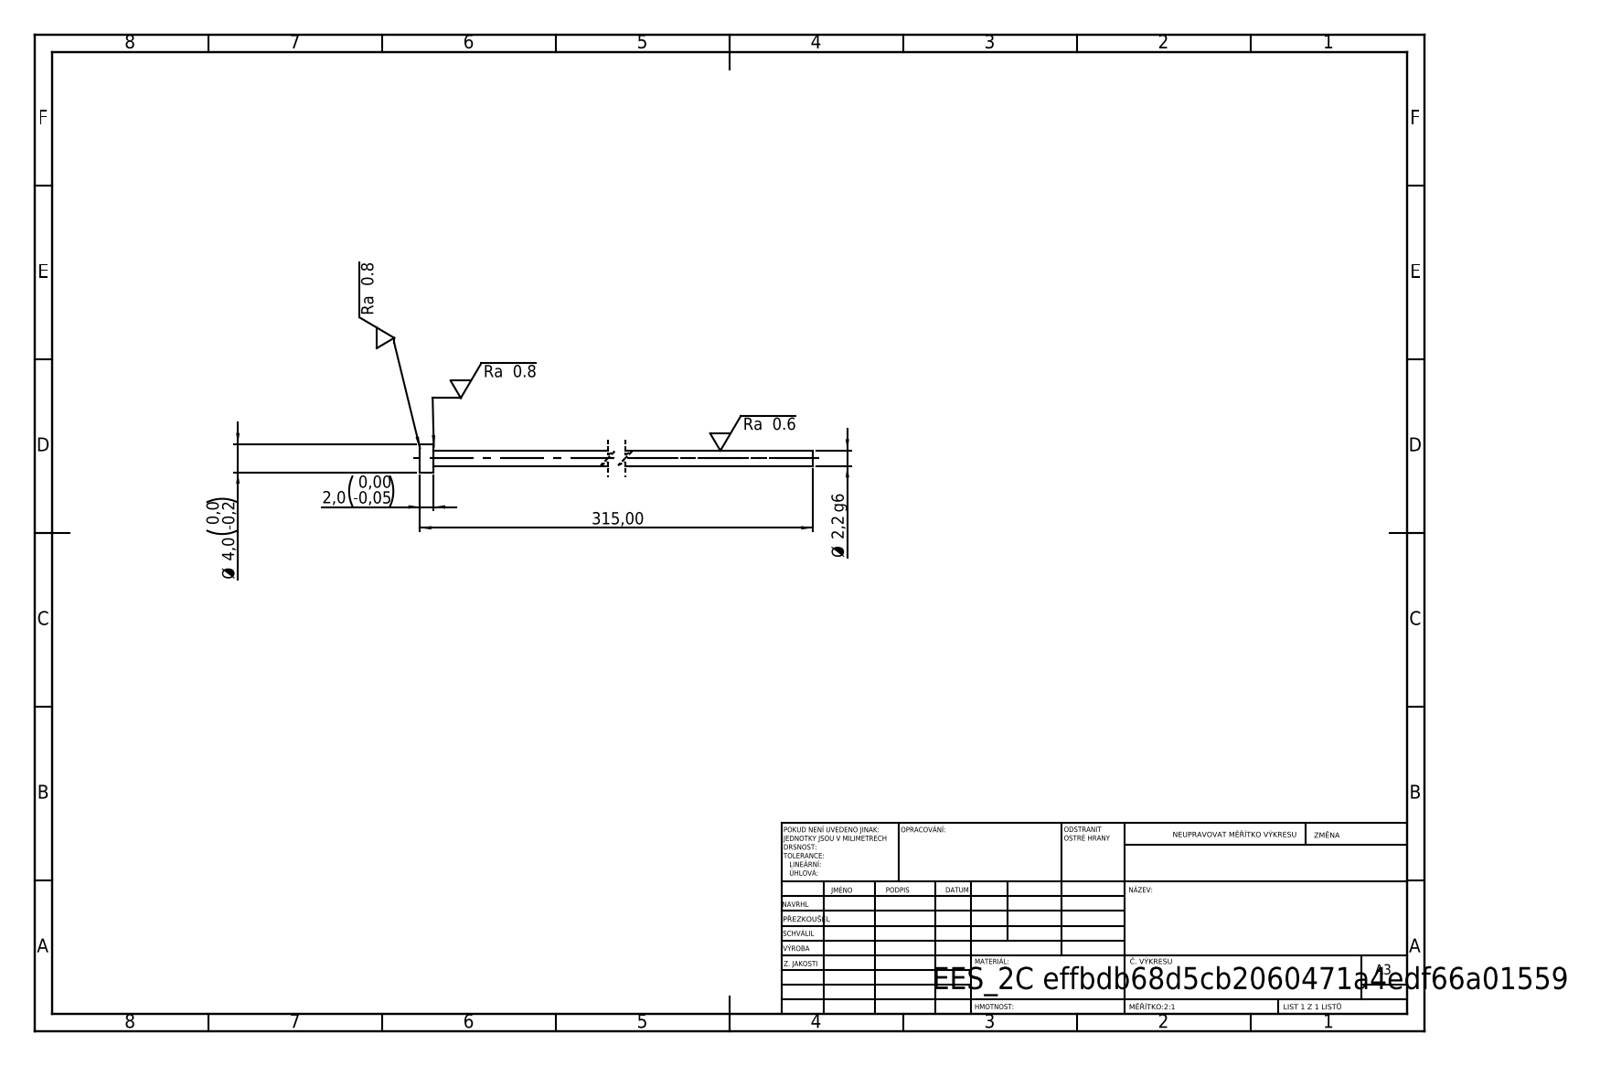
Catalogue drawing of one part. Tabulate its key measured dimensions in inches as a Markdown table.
| quantity | value |
| --- | --- |
| STEP written by | SolidWorks 2019 (CONFIG_CONTROL_DESIGN) |
| units | inches |
| bodies | 1 solid, 7 faces (3 planar, 4 cylindrical, 0 other) |
| overall size | 12.402 × 0.157 × 0.157 |
| volume | 0.074 in³ |
| surface area | 3.432 in² |
| round bosses / shafts (diameter × count) | 0.157 × 1, 0.087 × 1 |
| main face-to-face distances | 0.079, 12.402, 12.323 |
